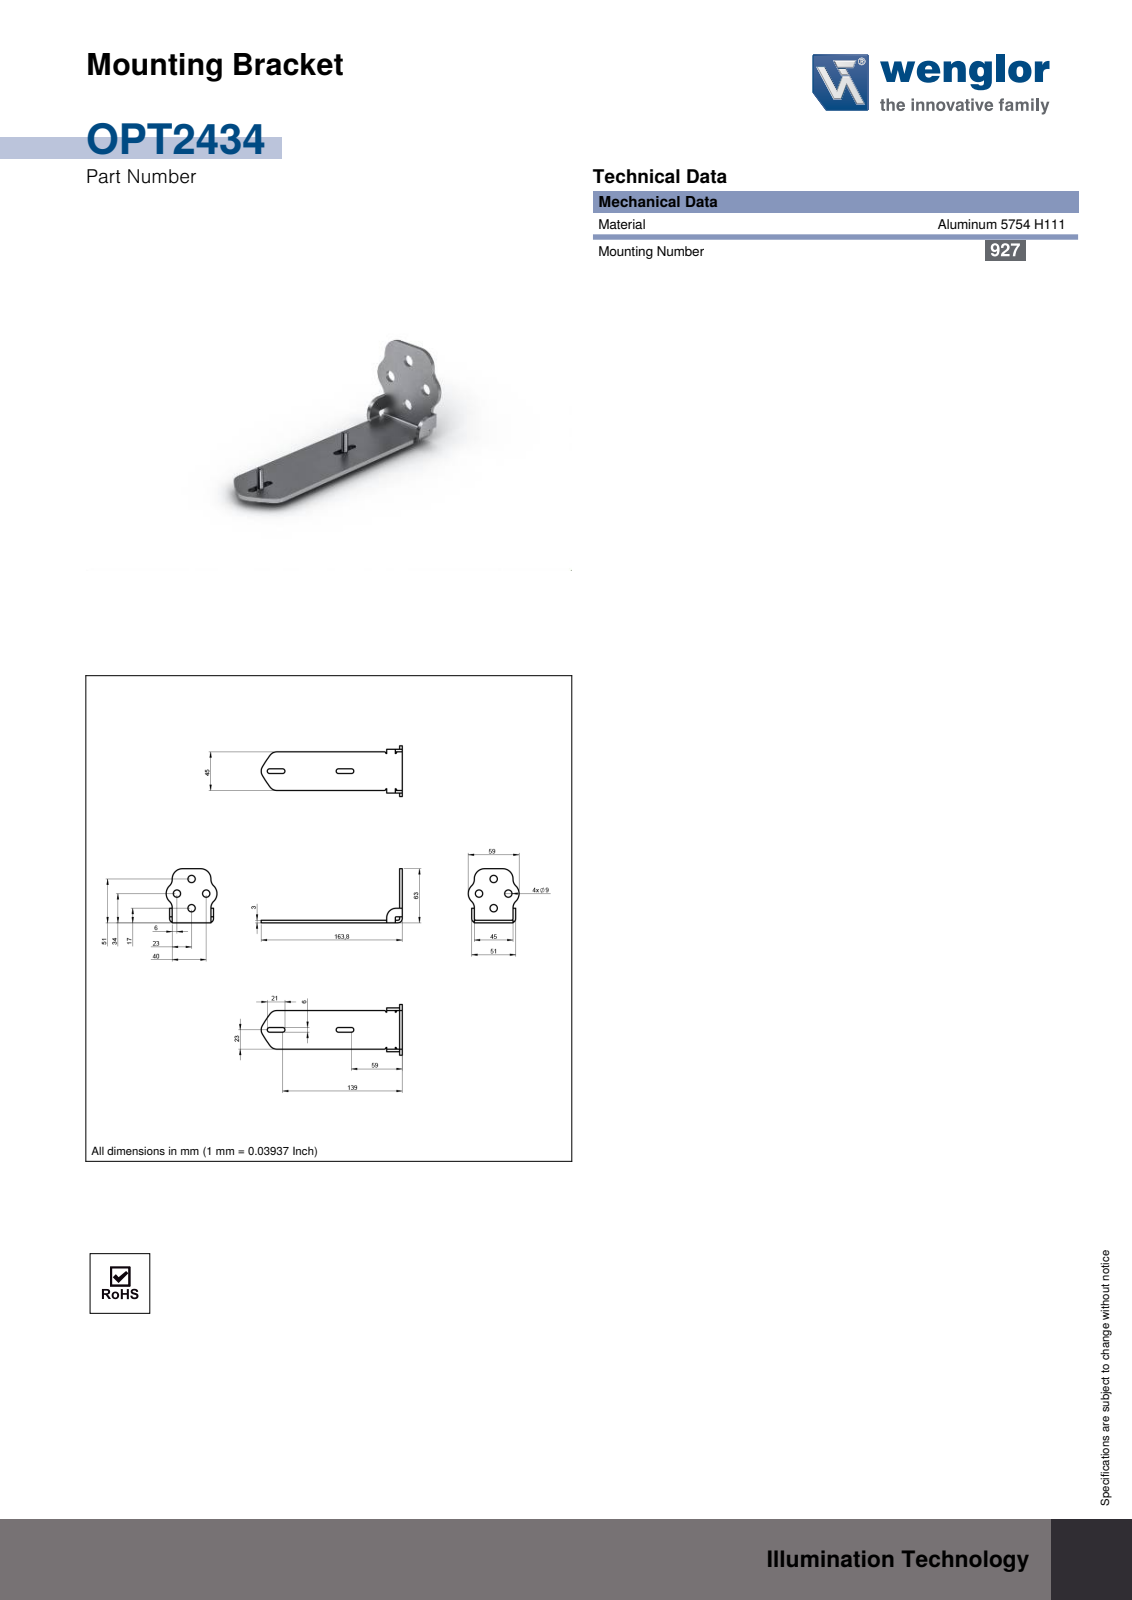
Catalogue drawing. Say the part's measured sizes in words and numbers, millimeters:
The part is named "OPT2434". Its 3-D file was written by "SolidWorks 2021 (AUTOMOTIVE_DESIGN)". It is 1 solid with 78 faces: 39 planar, 39 cylindrical and 0 other. Overall it measures 163.8 by 63 by 59 millimeters. Its volume is 29 640 cubic millimeters and its surface area 22 190 square millimeters. Round holes: 4 of diameter 8.5. Partial cylindrical surfaces (rounded edges, fillets, slot ends): 7 of radius 2, 6 of radius 10, 4 of radius 0.5, 4 of radius 2.7, 3 of radius 5, 2 of radius 12, 2 of radius 12.5, 2 of radius 140.7. The main face-to-face distances are 3, 45, 48, 22.8, 28.2, 19.8, 25.2, 51, 5.5, 10. The hole center spacings are 24, 34.
